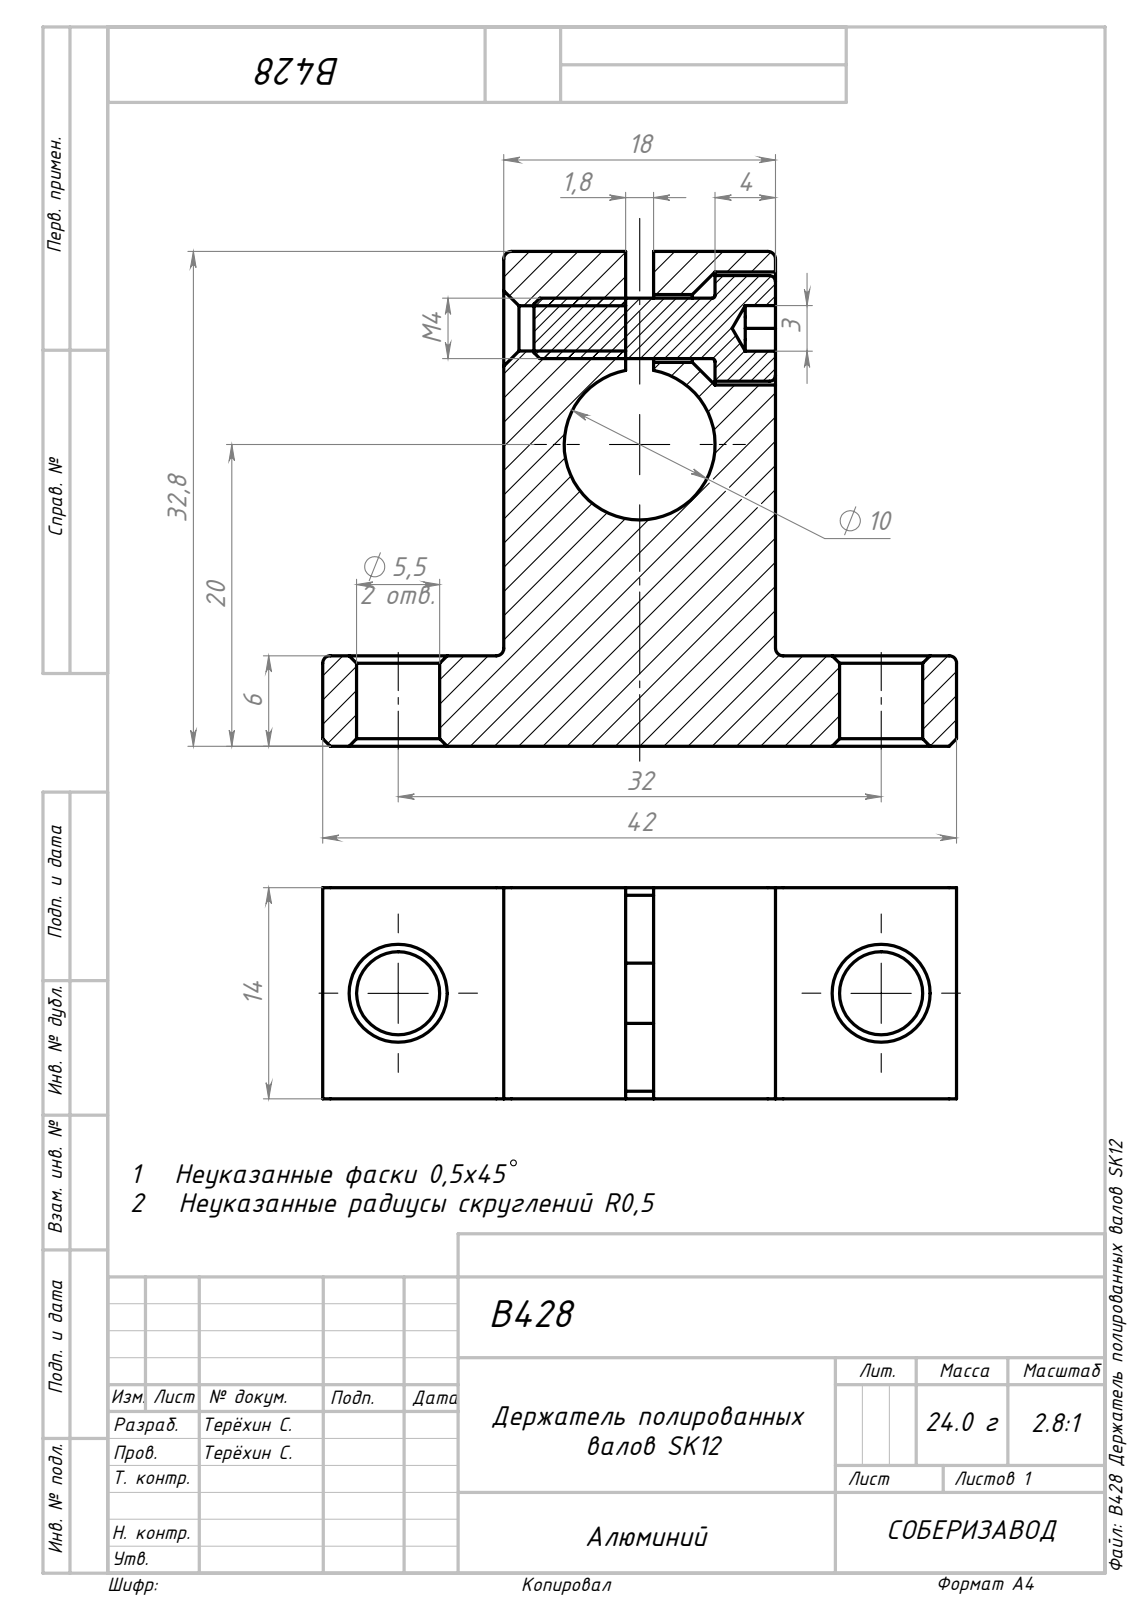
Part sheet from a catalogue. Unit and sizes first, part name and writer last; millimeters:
Units: millimetres
Overall size (bounding box): 42 × 32.8 × 14
Round holes (diameter × count): ⌀5.5 ×2, ⌀3 ×1, ⌀4.5 ×1, ⌀7.5 ×1, ⌀10 ×1
Round bosses / shafts (diameter × count): ⌀7 ×1, ⌀4 ×1
Partial cylindrical surfaces — rounded edges, fillets, slot ends (radius × count): R0.5 ×6
Main face-to-face distances: 14, 18, 6, 32.8, 26.8, 12, 30, 8.08, 9.92, 9.93
Hole centre spacings: 32
Volume: 8 634 mm³ · Surface area: 4 533 mm²
Bodies: 2 solids, 79 faces (30 planar, 23 cylindrical, 26 other)
Part name (STEP PRODUCT): B428 Держатель полированных валов SK12_00; socket head cap screw_din_DIN 912 M4 x 12 --- 12N; Сборка1
STEP written by: SolidWorks 2022 (AUTOMOTIVE_DESIGN)
